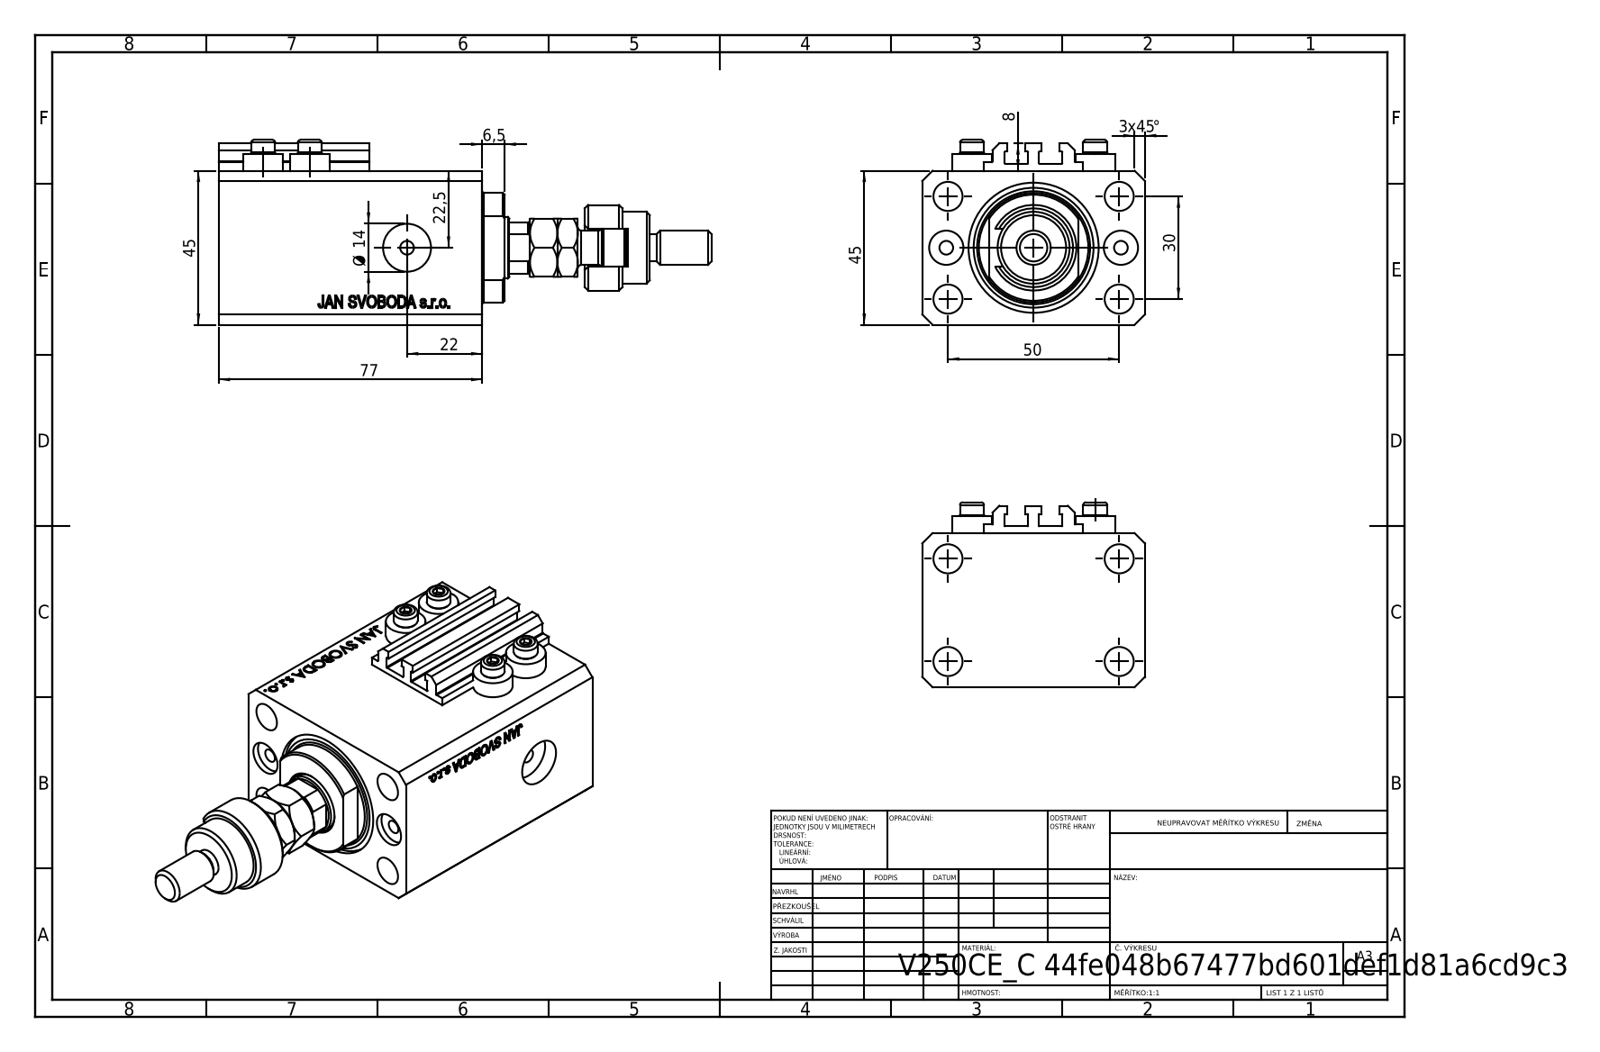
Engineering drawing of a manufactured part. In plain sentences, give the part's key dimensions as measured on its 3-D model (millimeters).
The part is named "V250CE_C_Body; MFA; V250CE_VC_C; FEMALE_PART_FOR_DFA (+2 more)". Its 3-D file was written by "SolidWorks 2019 (CONFIG_CONTROL_DESIGN)". It is 10 solids with 1118 faces: 531 planar, 99 cylindrical and 488 other. Overall it measures 143.9 by 65 by 54 millimeters. Its volume is 223 683 cubic millimeters and its surface area 64 869 square millimeters. Round holes: 8 of diameter 4, 5 of diameter 8.5, 2 of diameter 10, 2 of diameter 14, 1 of diameter 18, 1 of diameter 38. Round bosses or shafts: 4 of diameter 11.6, 4 of diameter 7, 1 of diameter 25, 1 of diameter 21, 1 of diameter 16, 1 of diameter 10, 1 of diameter 8. Partial cylindrical surfaces (rounded edges, fillets, slot ends): 10 of radius 0.2, 1 of radius 5.5, 1 of radius 8.5, 1 of radius 8.75, 1 of radius 16. The main face-to-face distances are 45, 65, 51.9, 77, 25.1, 3, 6.9, 70.1, 14, 2. The hole center spacings are 15.01, 29.15, 52.68, 13.6, 25.5, 30, 36, 38.48.
